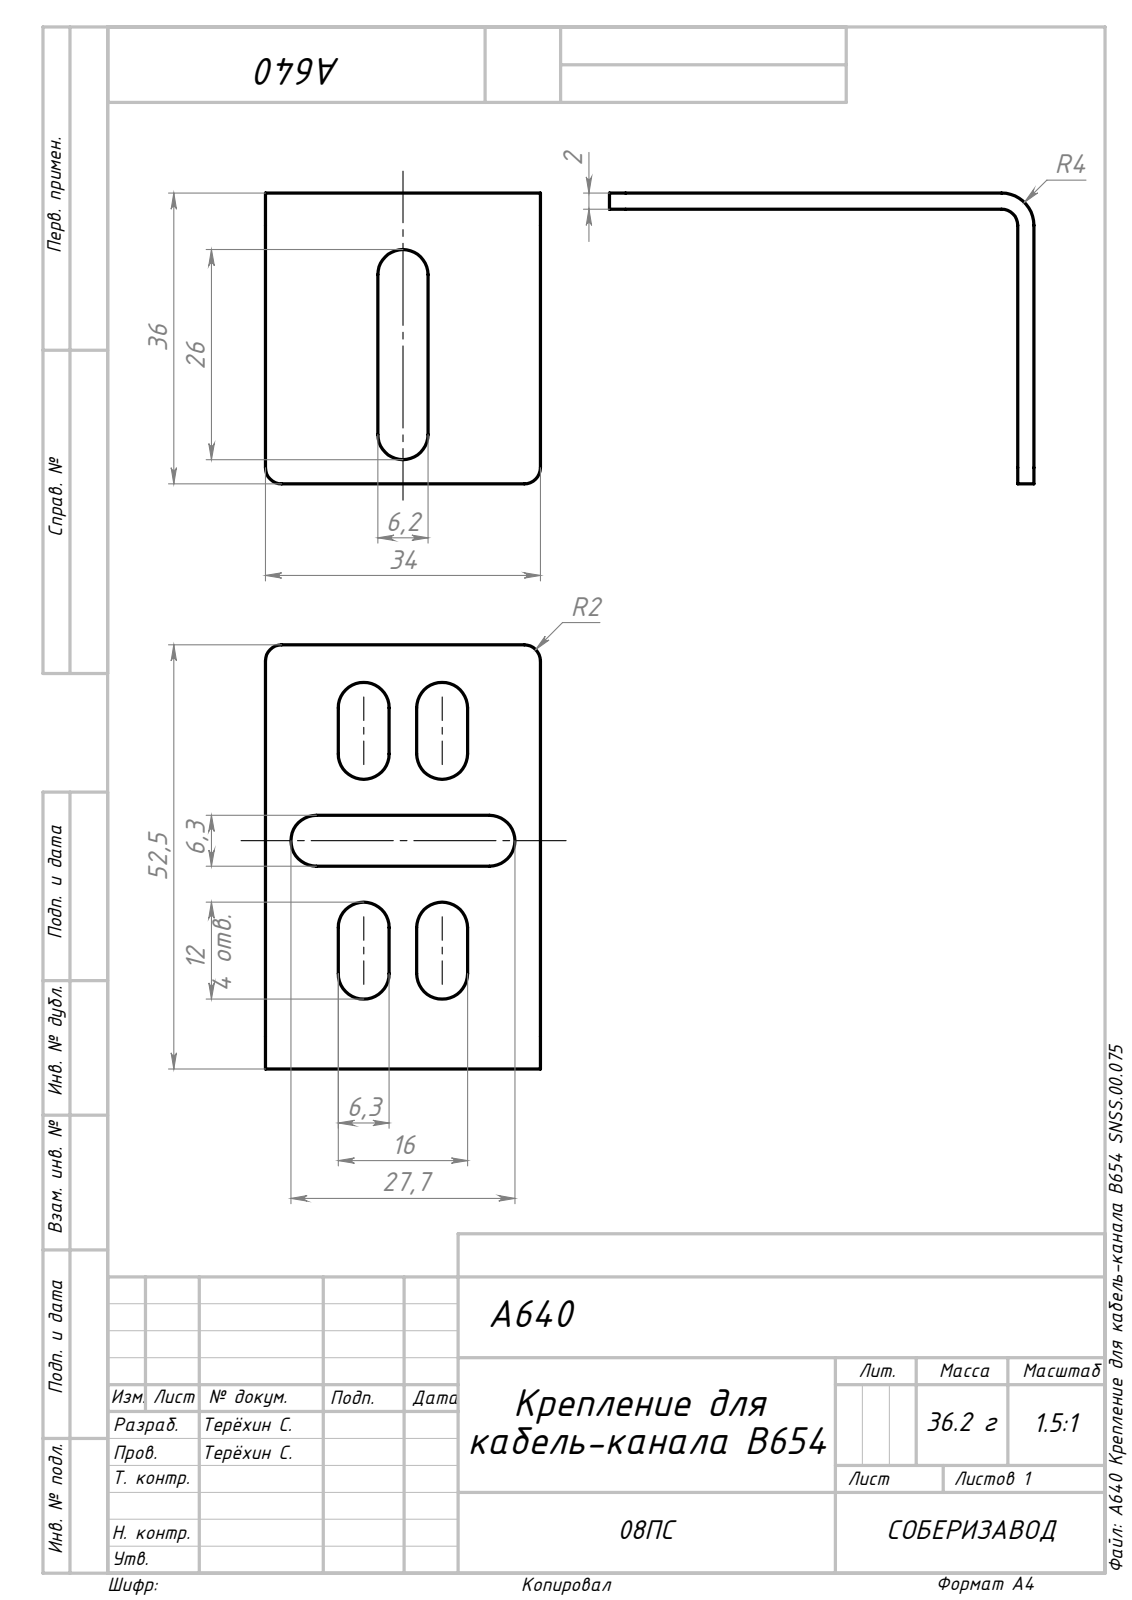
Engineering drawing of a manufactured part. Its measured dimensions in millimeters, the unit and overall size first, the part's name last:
Units: millimetres
Overall size (bounding box): 52.5 × 36 × 34
Partial cylindrical surfaces — rounded edges, fillets, slot ends (radius × count): R3.15 ×10, R2 ×5, R3.1 ×2, R4 ×1
Main face-to-face distances: 2, 34, 6.3, 13.9, 20.1, 36, 50.5, 52.5, 9, 25
Volume: 4 613 mm³ · Surface area: 5 576 mm²
Bodies: 1 solid, 47 faces (24 planar, 23 cylindrical, 0 other)
Part name (STEP PRODUCT): A640 Крепление для кабель-канала B654 SNSS.00.075_1; Сборка1
STEP written by: SolidWorks 2022 (AUTOMOTIVE_DESIGN)
